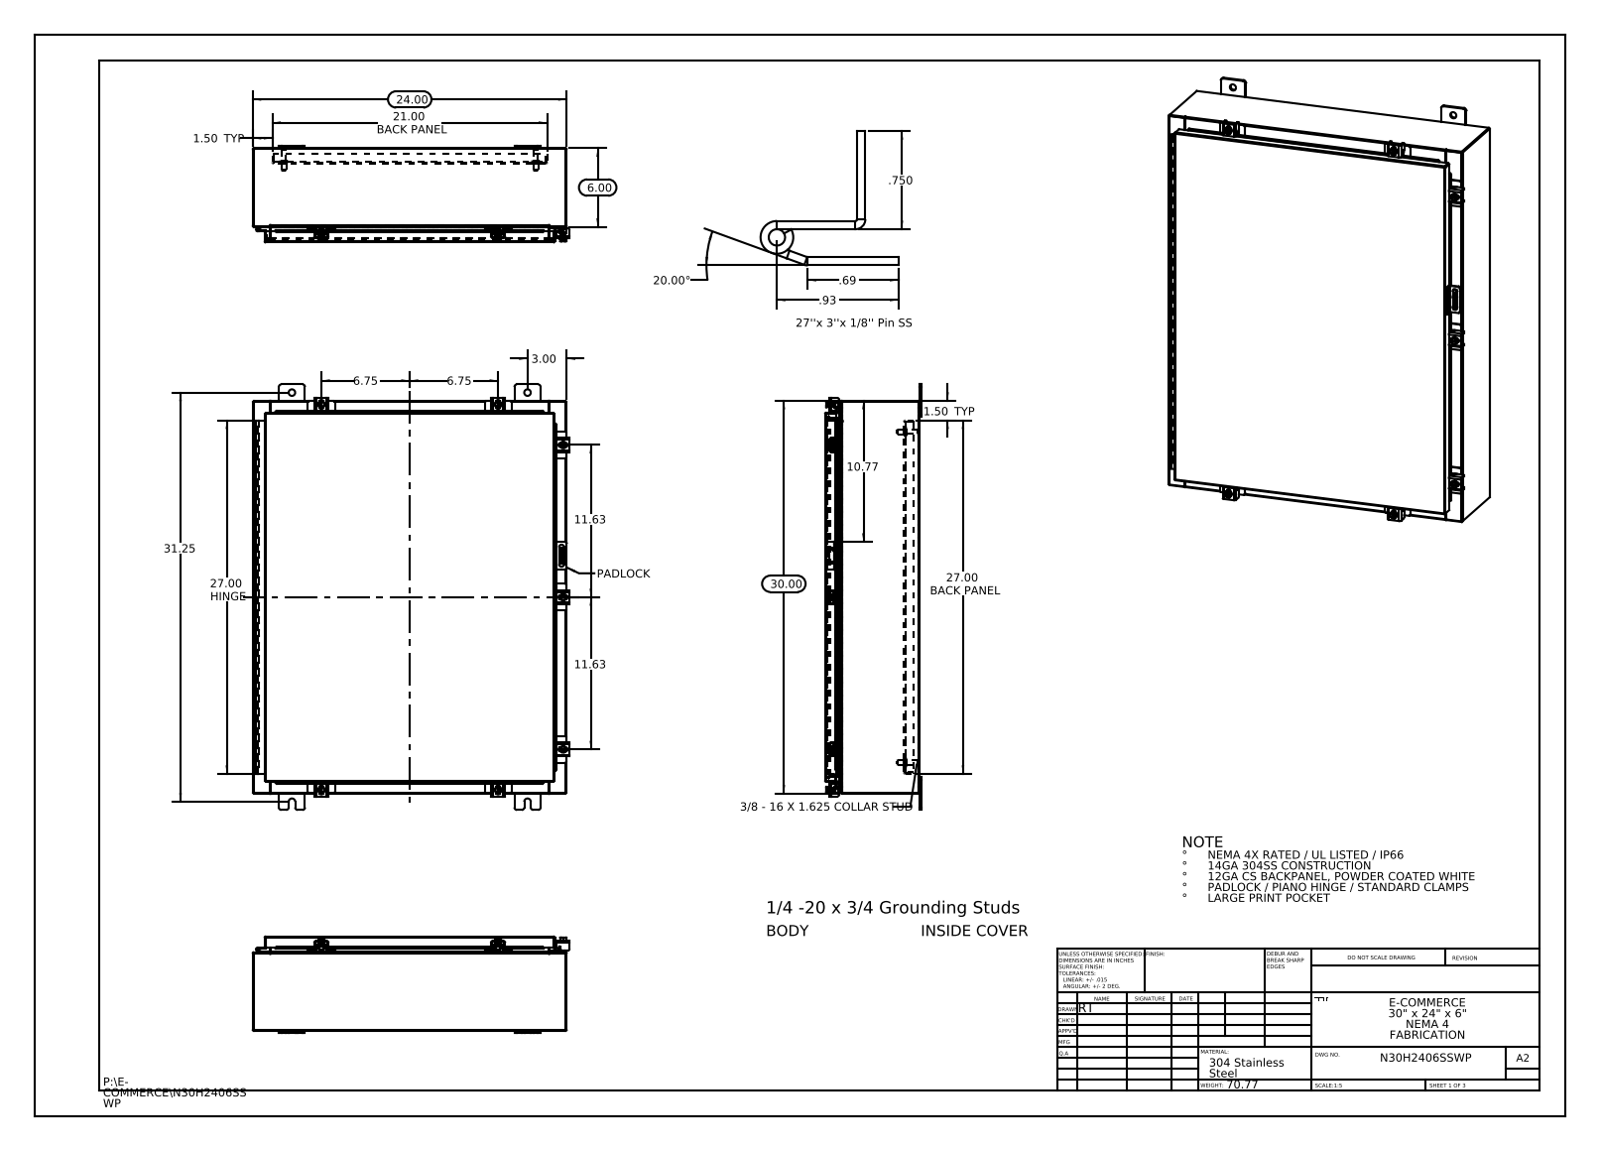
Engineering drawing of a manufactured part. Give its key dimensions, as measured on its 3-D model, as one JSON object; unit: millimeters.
{"part_name": "N30H2406SSWP Clamp Assembly; N30H2406SSWP; N30H2406SSWP Padlock Hasp; N30H2406SSWP Standard Clamps (+8 more)", "step_written_by": "SolidWorks 2013 (CONFIG_CONTROL_DESIGN)", "units": "millimeters", "bodies": {"solids": 52, "faces": 1990, "planar": 1056, "cylindrical": 830, "other": 104}, "overall_size": [825.5, 615, 187.7], "volume_mm3": 4077000, "surface_area_mm2": 3992000, "round_holes": [[12.7, 8], [5.4, 7], [6.6, 7], [3.2, 2], [3.2, 1]], "round_bosses_or_shafts": [[6.4, 8], [12.7, 7], [10.1, 7], [15.9, 4], [9.5, 4], [8.4, 4]], "partial_cylinders_radius": [[1.5, 34], [0.3, 27], [4.8, 24], [2.2, 21], [3, 14], [3.6, 14], [1.3, 11], [2, 10]], "face_to_face_distances": [1.9, 181, 182.9, 179.1, 2.6, 25.4, 27.3, 153.7, 155.6, 29.9], "hole_center_spacings": [698.5, 809.7, 47.2, 57.8, 59.1, 61.5, 90.4, 90.4]}
